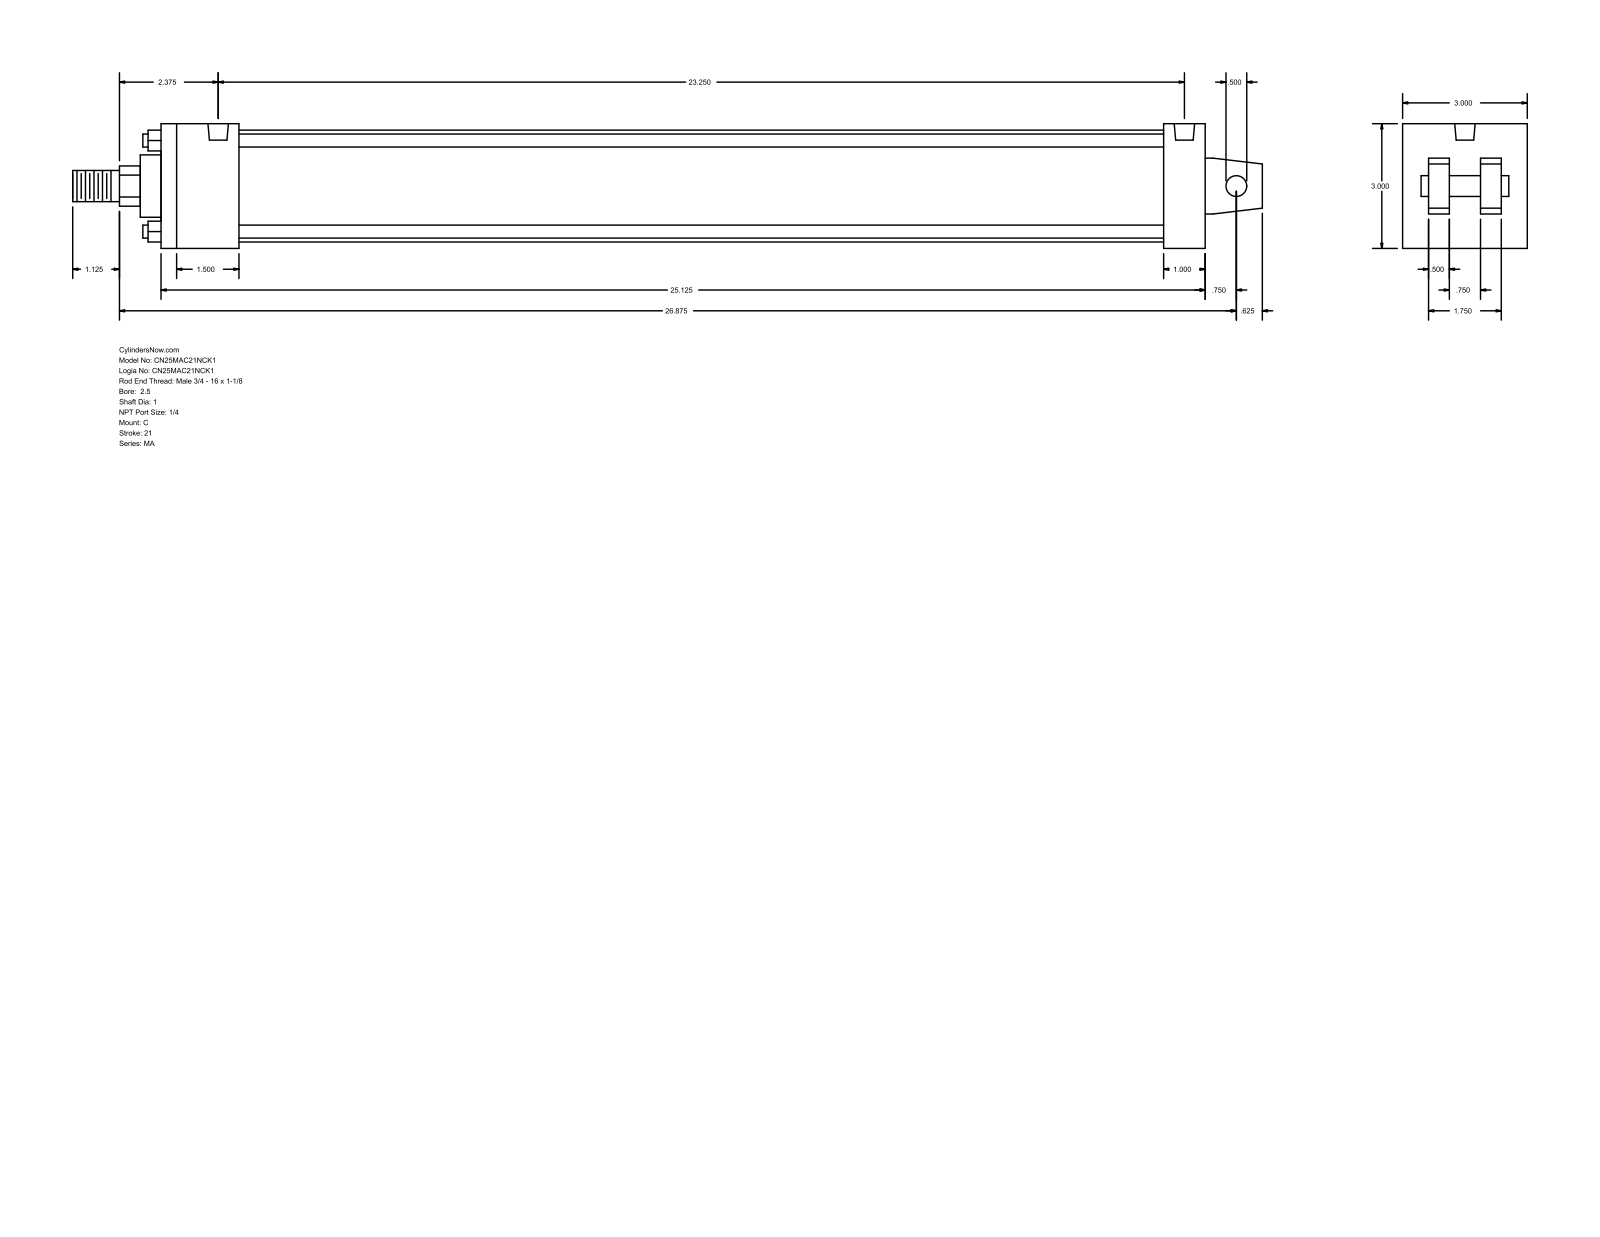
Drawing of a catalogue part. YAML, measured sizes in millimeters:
part_name: "MA_C__0250_1"
step_written_by: "GSSL Pune (CONFIG_CONTROL_DESIGN)"
units: millimeters
bodies: {solids: 0, faces: 103, planar: 76, cylindrical: 27, other: 0}
overall_size: [727.08, 76.2, 76.2]
round_holes:
  - {diameter: 7.94, count: 4}
  - {diameter: 12.49, count: 2}
round_bosses_or_shafts:
  - {diameter: 7.94, count: 4}
  - {diameter: 68.33, count: 1}
  - {diameter: 38.1, count: 1}
  - {diameter: 25.4, count: 1}
  - {diameter: 19.05, count: 1}
  - {diameter: 12.7, count: 1}
partial_cylinders:
  - {radius: 12.29, count: 1}
face_to_face_distances: [76.2, 47.63, 638.18, 12.7, 60.33, 15.87, 28.57, 612.77, 565.14, 590.55]
hole_center_spacings: [590.55]
